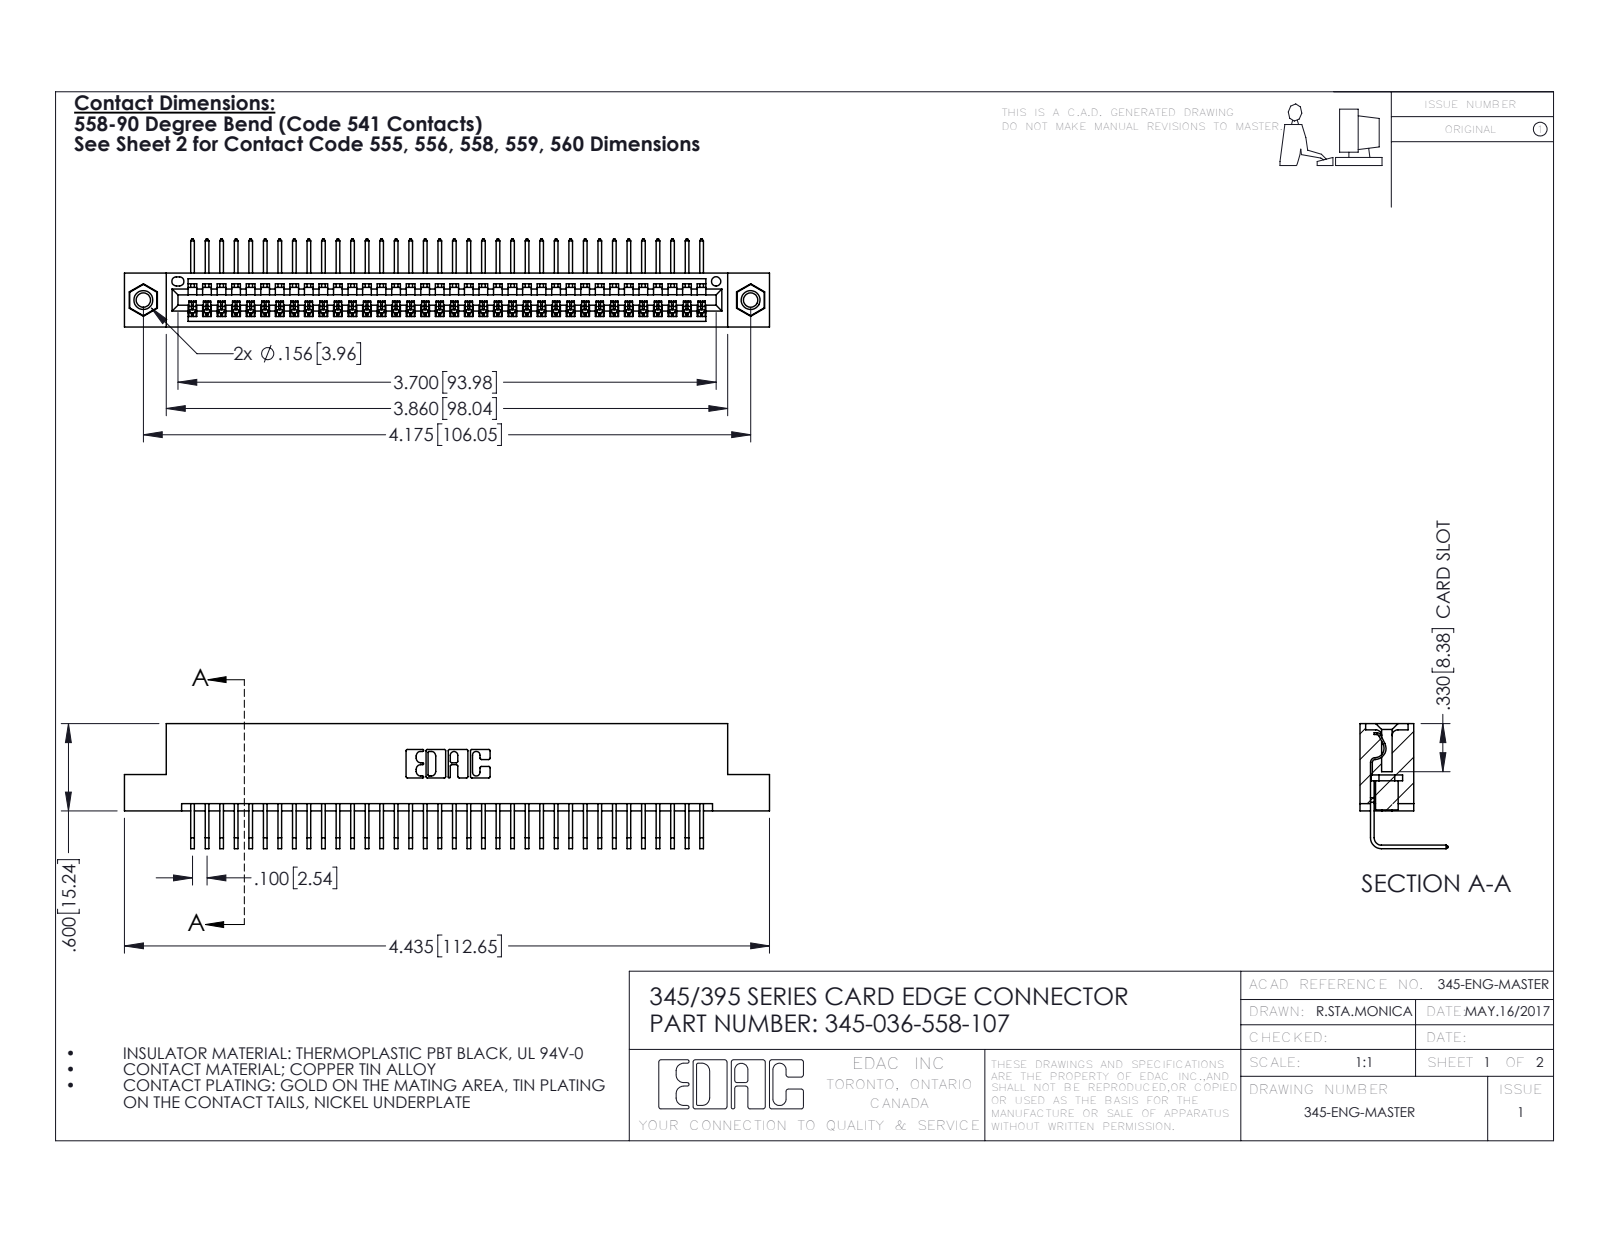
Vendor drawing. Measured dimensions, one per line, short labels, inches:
name: 345-036-558-107; 345 Part_Flush Mounting Lugs - 0.156 Dia-TI; 345-250-001_345-250-005-103; 345-292-001_558 Tail - 2
written by: SolidWorks 2016 (CONFIG_CONTROL_DESIGN)
unit: in
bodies: 39 solids, 2346 faces (1624 planar, 706 cylindrical, 16 other)
size: 4.435 × 0.859 × 0.605
volume: 0.656 in³; area: 23.17 in²
holes: 2× ⌀0.098, 2× ⌀0.125, 2× ⌀0.156, 1× ⌀0.064
bosses: 2× ⌀0.155
rounds: 72× R0.006, 22× R0.01, 6× R0.007, 6× R0.031, 3× R0.026, 2× R0.031, 2× R0.04, 1× R0.014
face distances: 0.072, 0.298, 0.37, 0.2, 0.098, 0.272, 0.025, 0.225, 0.149, 0.072
hole spacings: 0.27, 3.939, 4.175
